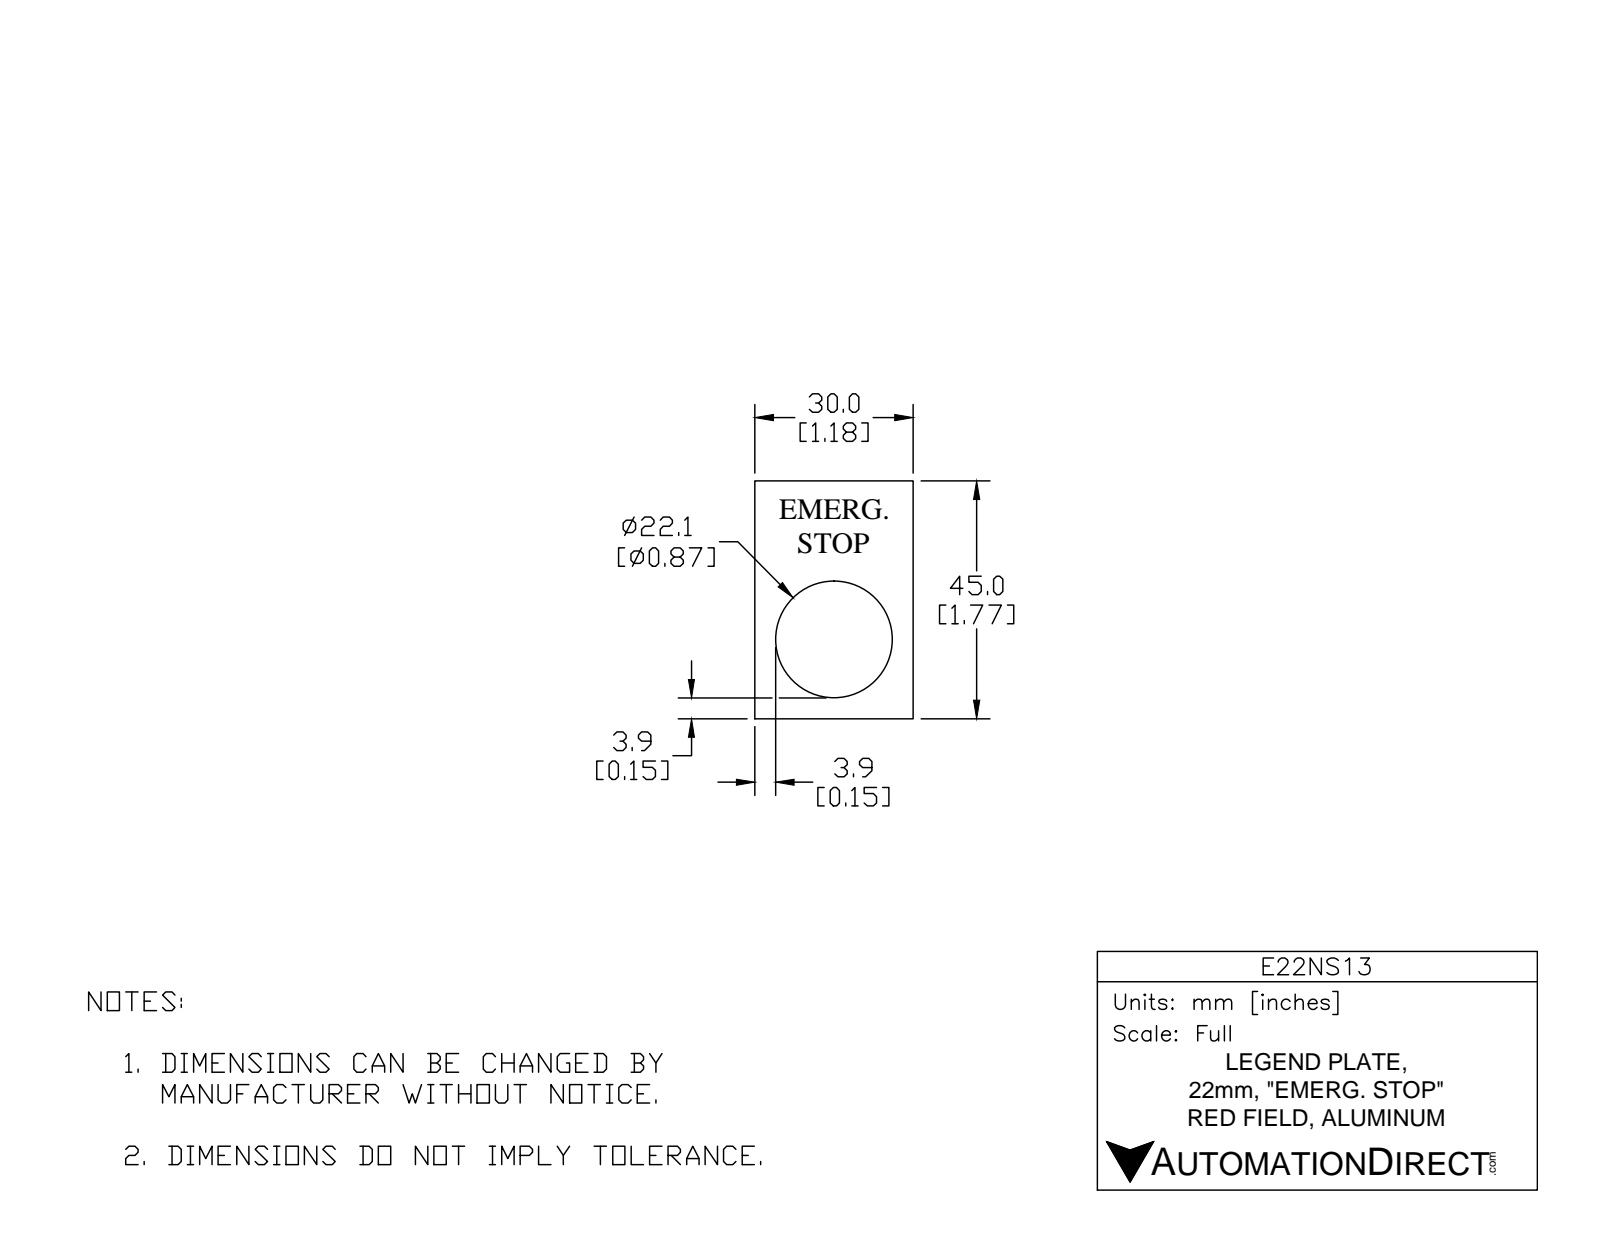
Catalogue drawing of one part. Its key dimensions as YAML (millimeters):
part_name: "E22NS13"
step_written_by: "SolidWorks 2017 (AUTOMOTIVE_DESIGN)"
units: millimeters
bodies: {solids: 1, faces: 142, planar: 92, cylindrical: 3, other: 47}
overall_size: [45, 30, 1.3]
volume: 1246
surface_area: 2266
round_holes:
  - {diameter: 22.2, count: 1}
face_to_face_distances: [1.3, 30, 45, 1.05, 0.36, 4.7, 40.3, 0.41, 4, 1.95]
